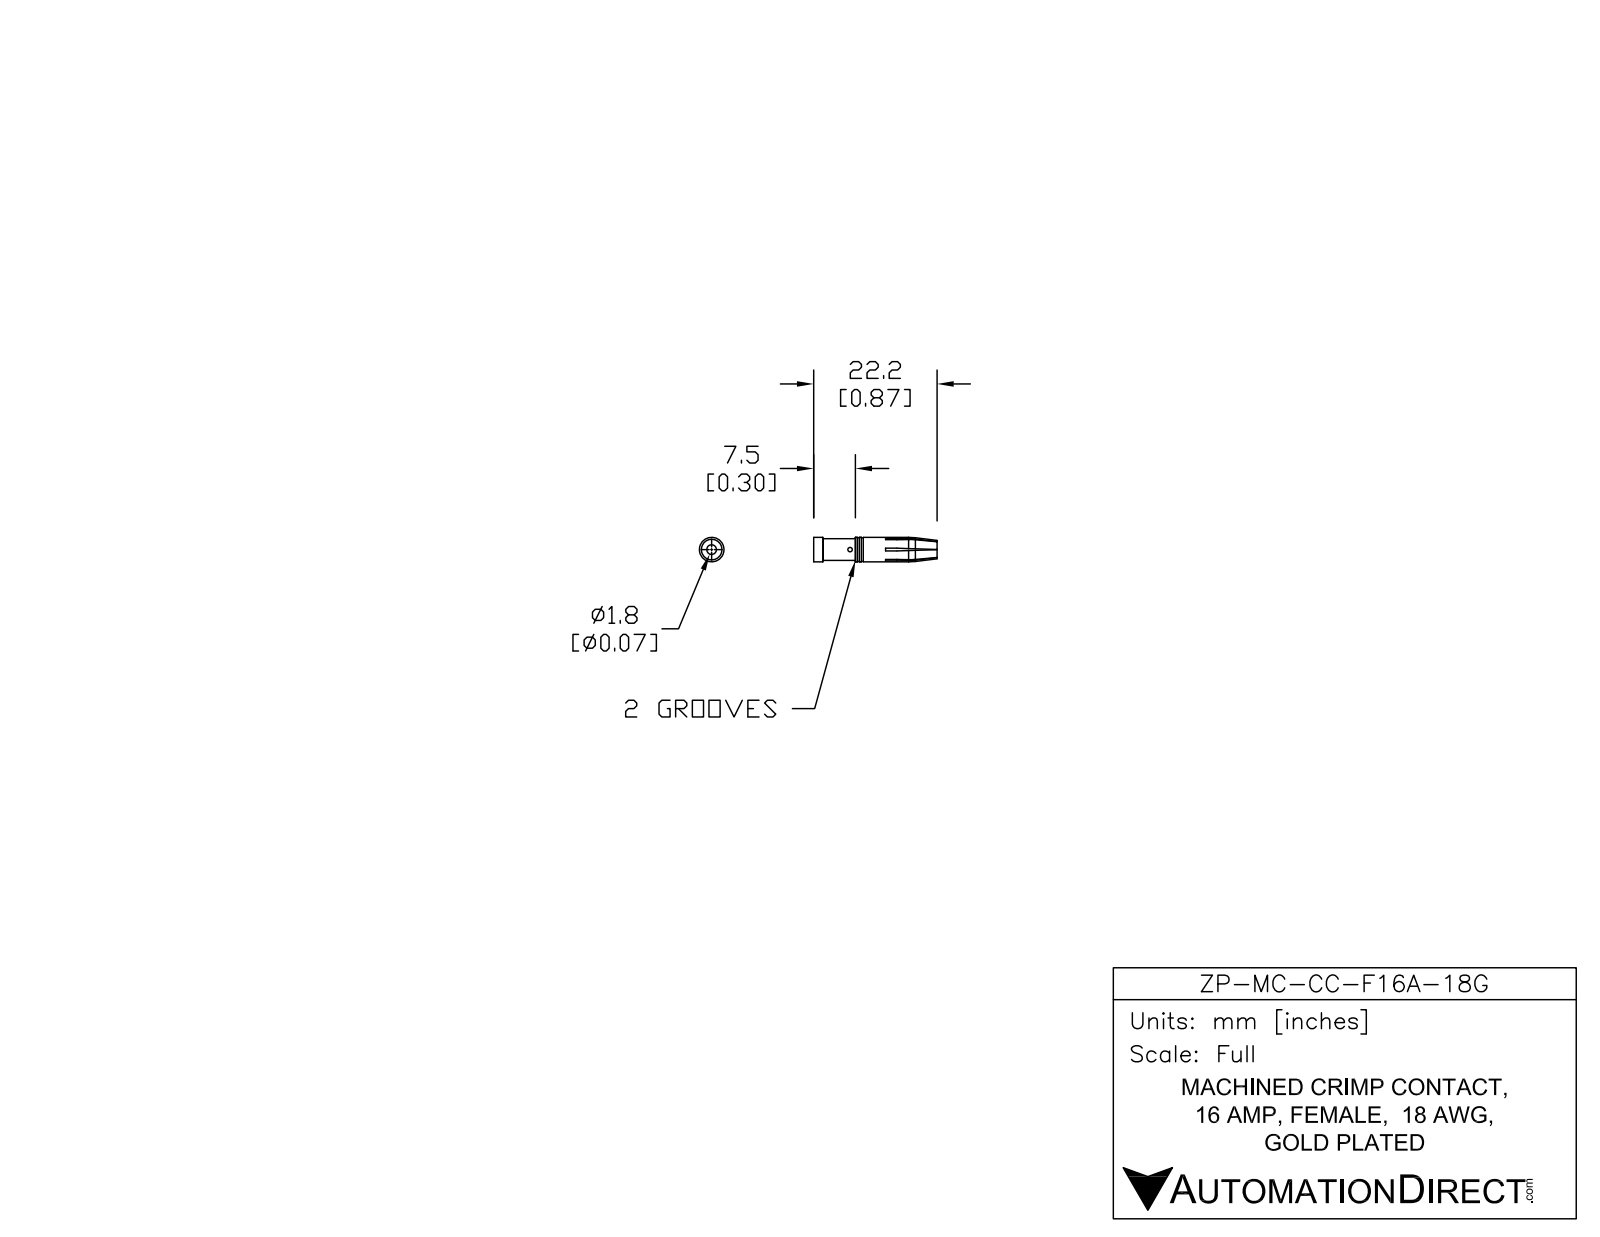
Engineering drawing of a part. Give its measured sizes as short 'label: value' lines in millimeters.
name: ZP-MC-CC-F16A-18G
written by: SolidWorks 2014 (AUTOMOTIVE_DESIGN)
unit: mm
bodies: 1 solid, 75 faces (37 planar, 14 cylindrical, 24 other)
size: 22.2 × 4.42 × 4.42
volume: 183 mm³; area: 489 mm²
holes: 1× ⌀0.8, 1× ⌀1.3
bosses: 1× ⌀4.42, 1× ⌀4.04, 1× ⌀2.66
face distances: 0.5, 14.7, 22.2, 7.5, 9.25, 5.45, 12.95, 21.39, 12.14, 6.69
